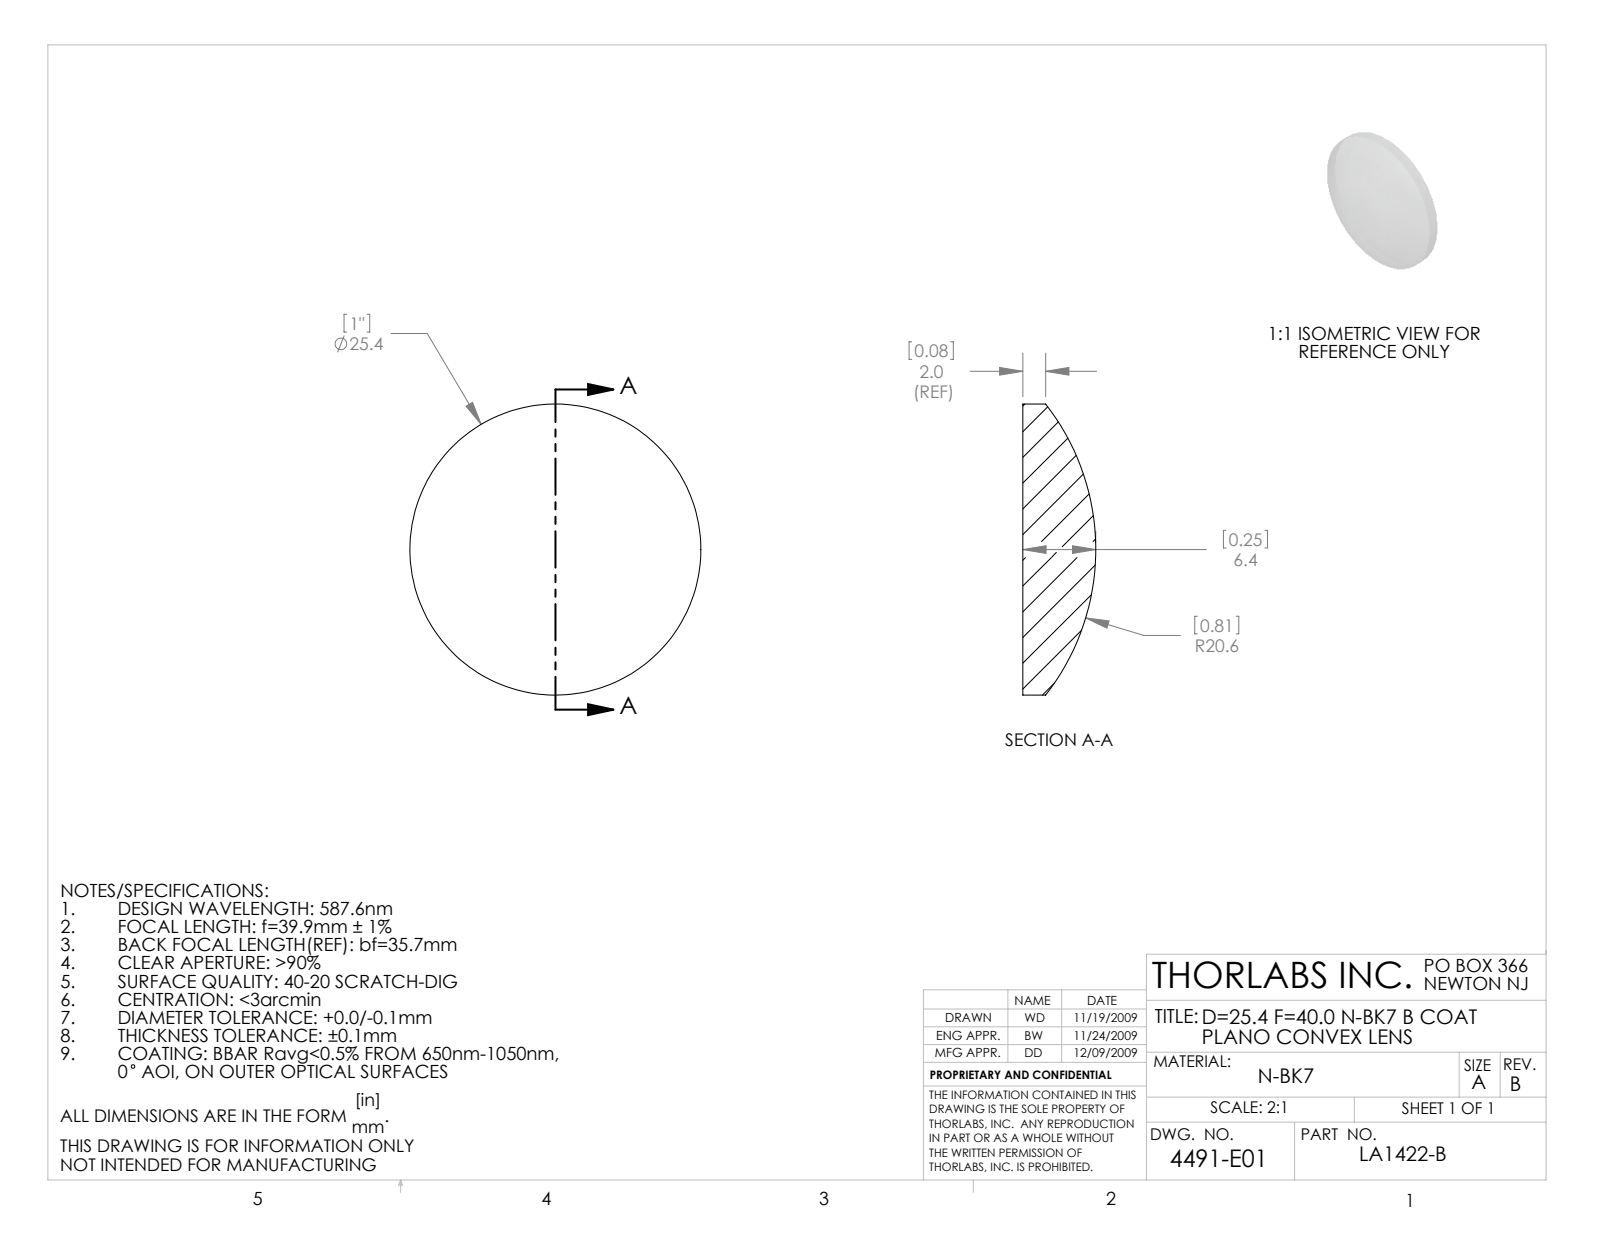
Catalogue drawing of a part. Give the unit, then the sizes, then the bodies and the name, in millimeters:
Units: millimetres
Overall size (bounding box): 25.4 × 25.4 × 6.37
Round bosses / shafts (diameter × count): ⌀25.4 ×1
Volume: 2 162 mm³ · Surface area: 1 232 mm²
Bodies: 1 solid, 5 faces (1 planar, 2 cylindrical, 2 other)
Part name (STEP PRODUCT): 4491-E0W
STEP written by: SolidWorks 2009 (AUTOMOTIVE_DESIGN)
